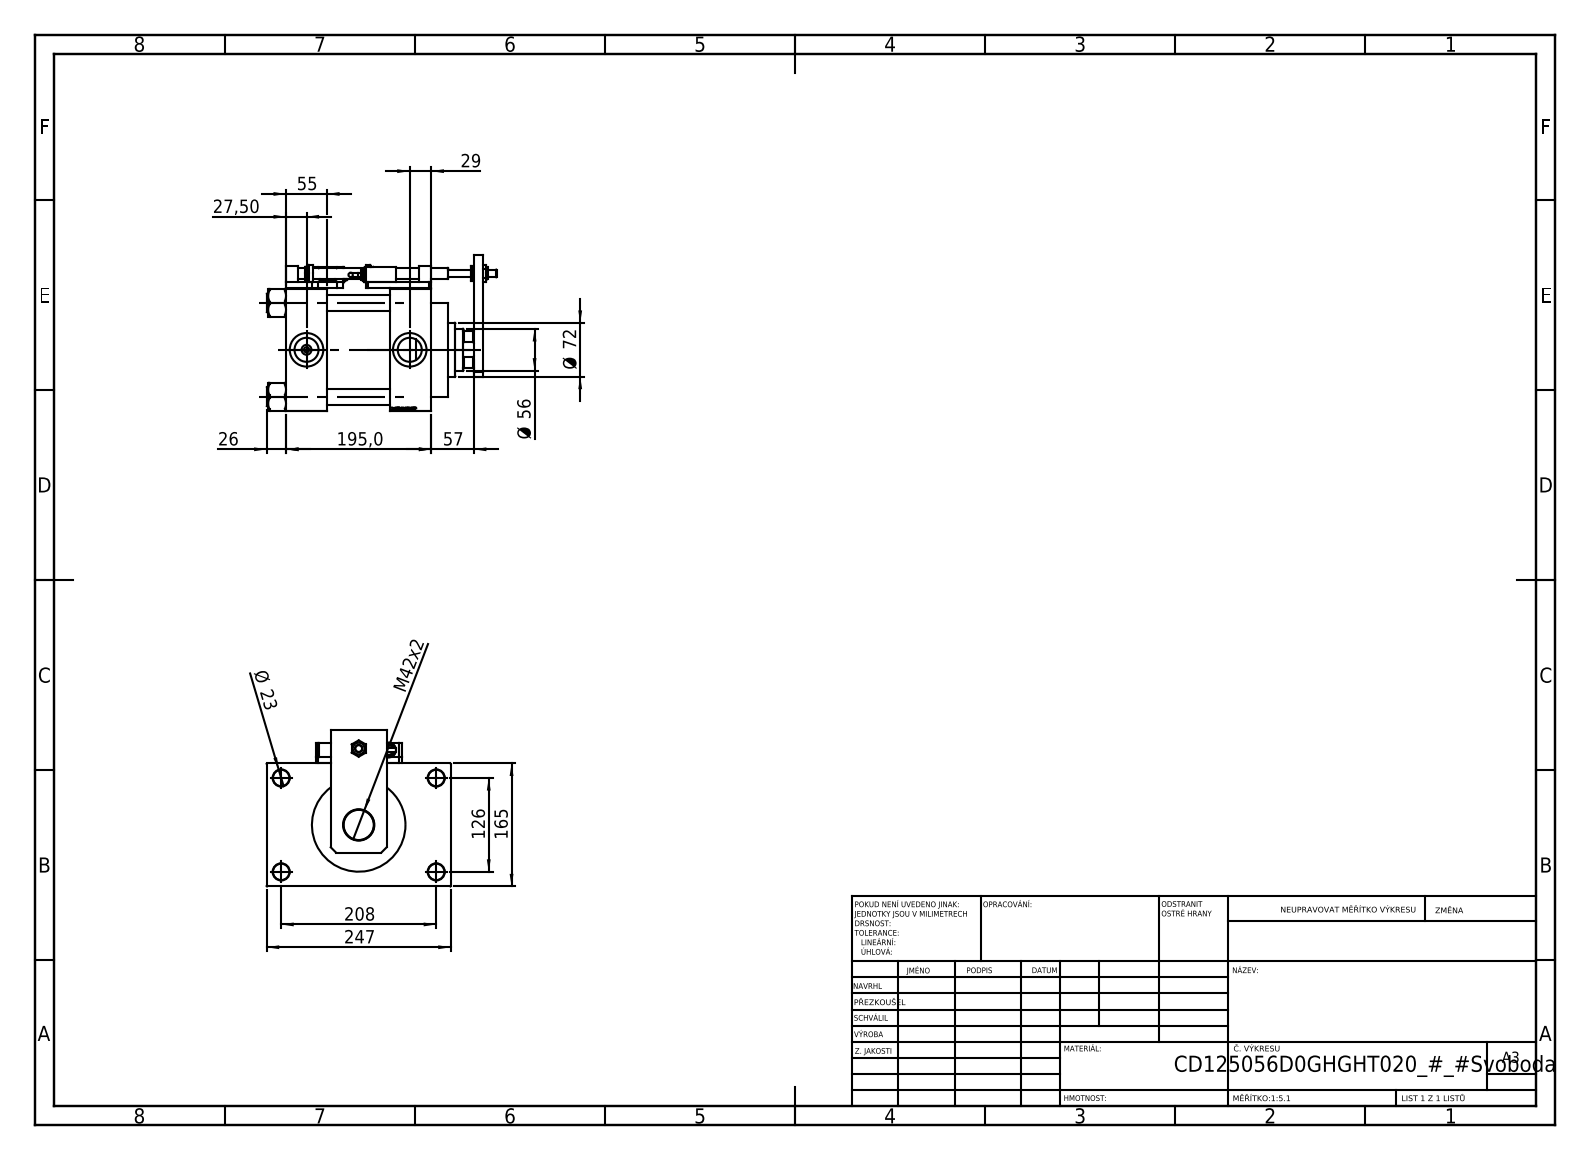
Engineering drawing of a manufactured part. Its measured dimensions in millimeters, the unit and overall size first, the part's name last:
Units: millimetres
Overall size (bounding box): 308.5 × 247 × 210
Round holes (diameter × count): ⌀22 ×8, ⌀8.5 ×4, ⌀13.5 ×4, ⌀7 ×2, ⌀32.24 ×2, ⌀45 ×2, ⌀10 ×1, ⌀14 ×1, ⌀40.5 ×1, ⌀42 ×1, ⌀56 ×1, ⌀59 ×1
Round bosses / shafts (diameter × count): ⌀25 ×4, ⌀20 ×3, ⌀16 ×2, ⌀14 ×2, ⌀6 ×2, ⌀131 ×1, ⌀72 ×1, ⌀23 ×1
Partial cylindrical surfaces — rounded edges, fillets, slot ends (radius × count): R7.5 ×4, R27 ×1
Main face-to-face distances: 140, 165, 55, 195, 84, 139, 56, 173, 8, 41
Hole centre spacings: 41.05, 89.02, 121.59, 125.9, 132.47, 166.95, 209.13, 32
Volume: 5 297 000 mm³ · Surface area: 640 290 mm²
Bodies: 24 solids, 1376 faces (665 planar, 154 cylindrical, 557 other)
Part name (STEP PRODUCT): V215CD_D_TYCINKA; V215CD_SWITCH_Q_ZARAZKA; V215CD_SWITCH_Q_SWITCH; V215CD_SWITCH_Q_PODLOZKA_BACK (+8 more)
STEP written by: SolidWorks 2019 (CONFIG_CONTROL_DESIGN)
